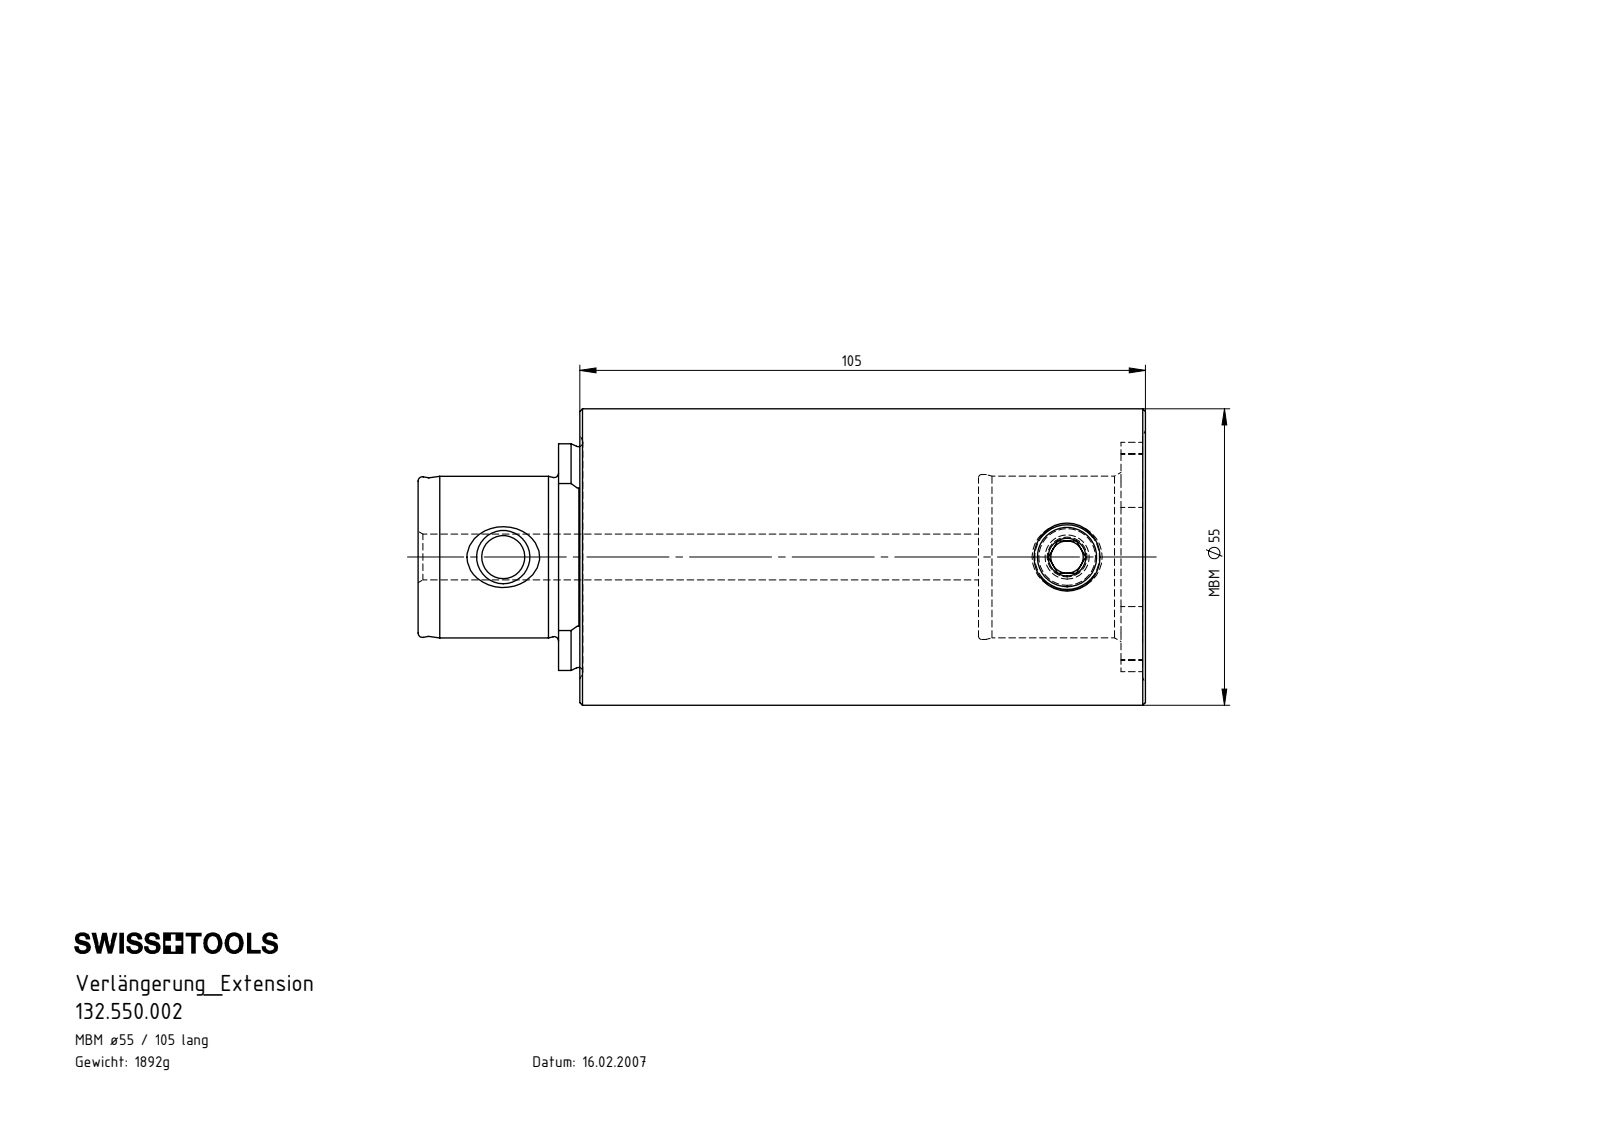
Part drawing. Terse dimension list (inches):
name: 132.550.002; MB5-ER1.001.017_A; MB5-MB5.K01.105_C
written by: SolidWorks 2017 (AUTOMOTIVE_DESIGN)
unit: in
bodies: 2 solids, 127 faces (32 planar, 32 cylindrical, 63 other)
size: 5.315 × 2.165 × 2.165
volume: 14.71 in³; area: 50.76 in²
holes: 1× ⌀0.236, 1× ⌀0.315, 1× ⌀0.335, 1× ⌀0.433, 1× ⌀1.181, 1× ⌀1.205
bosses: 1× ⌀2.165, 1× ⌀0.472
rounds: 4× R0.205, 1× R0.728, 1× R0.828, 1× R0.837
face distances: 2.913, 4.134, 1.22, 1.181, 4.094, 5.315, 5.136, 3.955, 1.041, 0.179
hole spacings: 4.12
